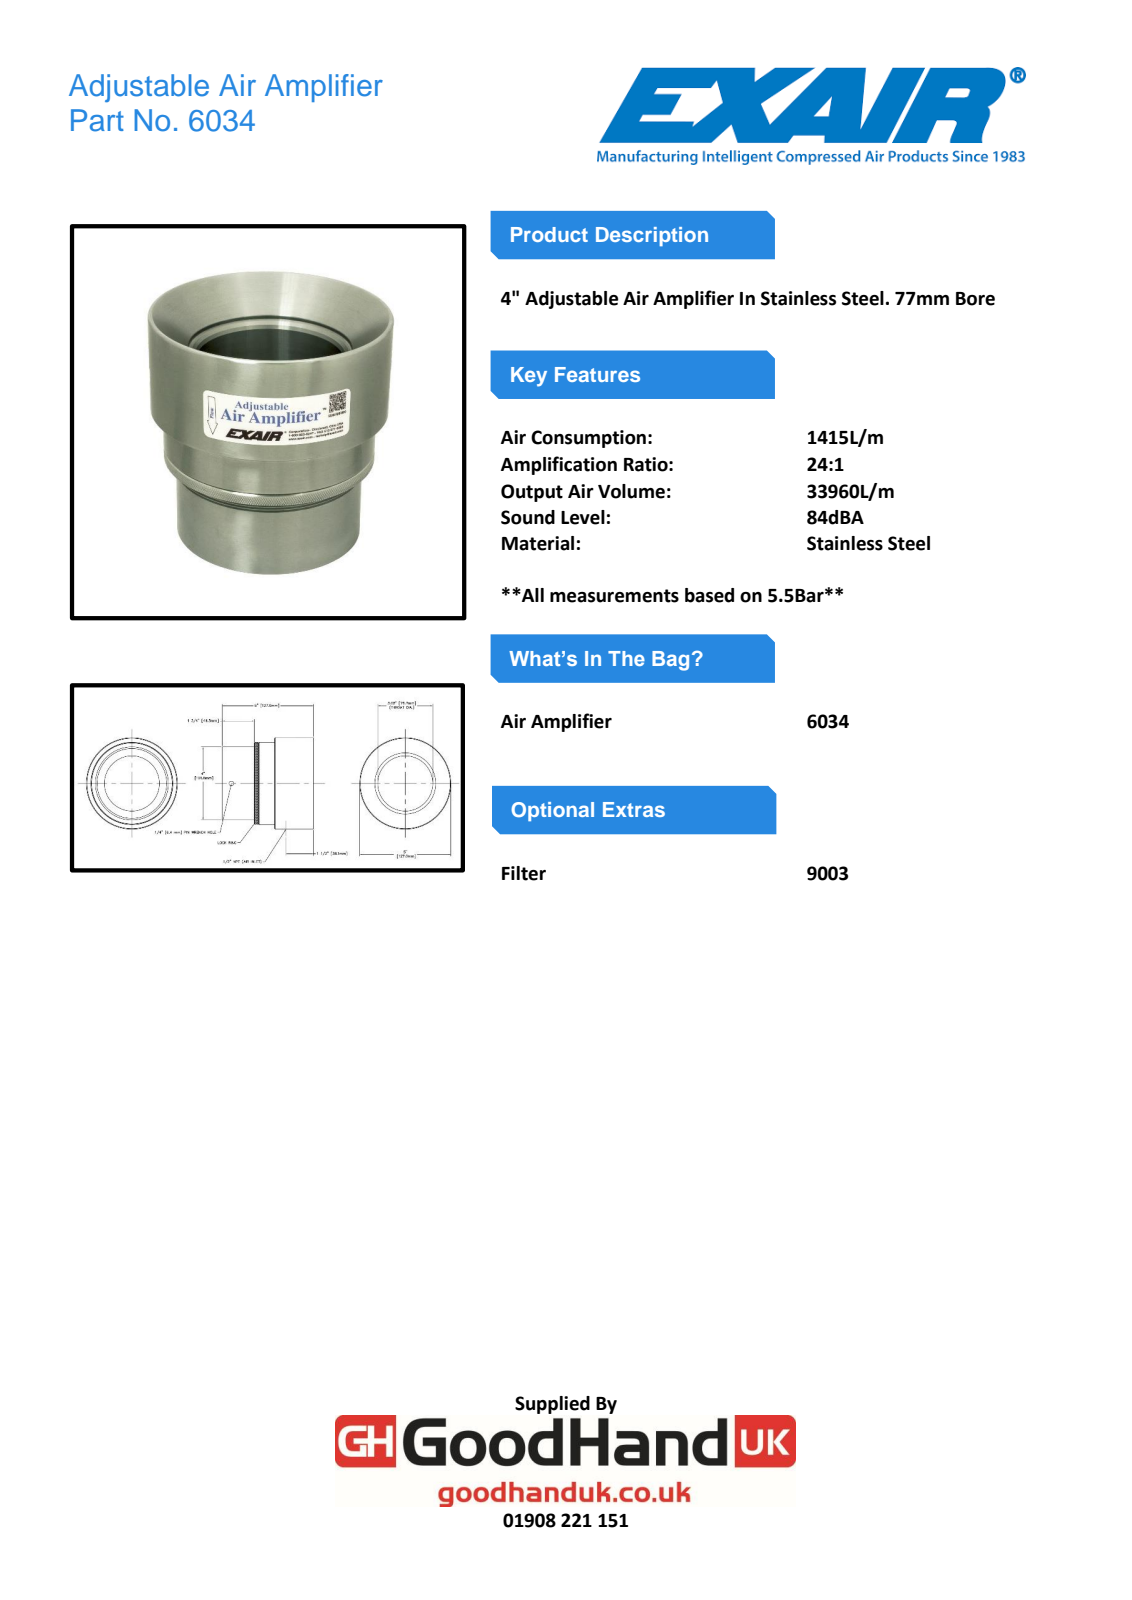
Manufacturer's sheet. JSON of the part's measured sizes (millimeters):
{"step_written_by": "Autodesk Inventor 2010 (AUTOMOTIVE_DESIGN)", "units": "millimeters", "bodies": {"solids": 1, "faces": 18, "planar": 4, "cylindrical": 7, "other": 7}, "overall_size": [127.1, 127.1, 126.3], "volume_mm3": 519600, "surface_area_mm2": 90450, "round_holes": [[6.4, 1], [21.3, 1], [81.4, 1]], "round_bosses_or_shafts": [[127, 1], [113.9, 1], [101.6, 1]], "face_to_face_distances": [27.8, 44.5, 72.3], "hole_center_spacings": [75.5]}
